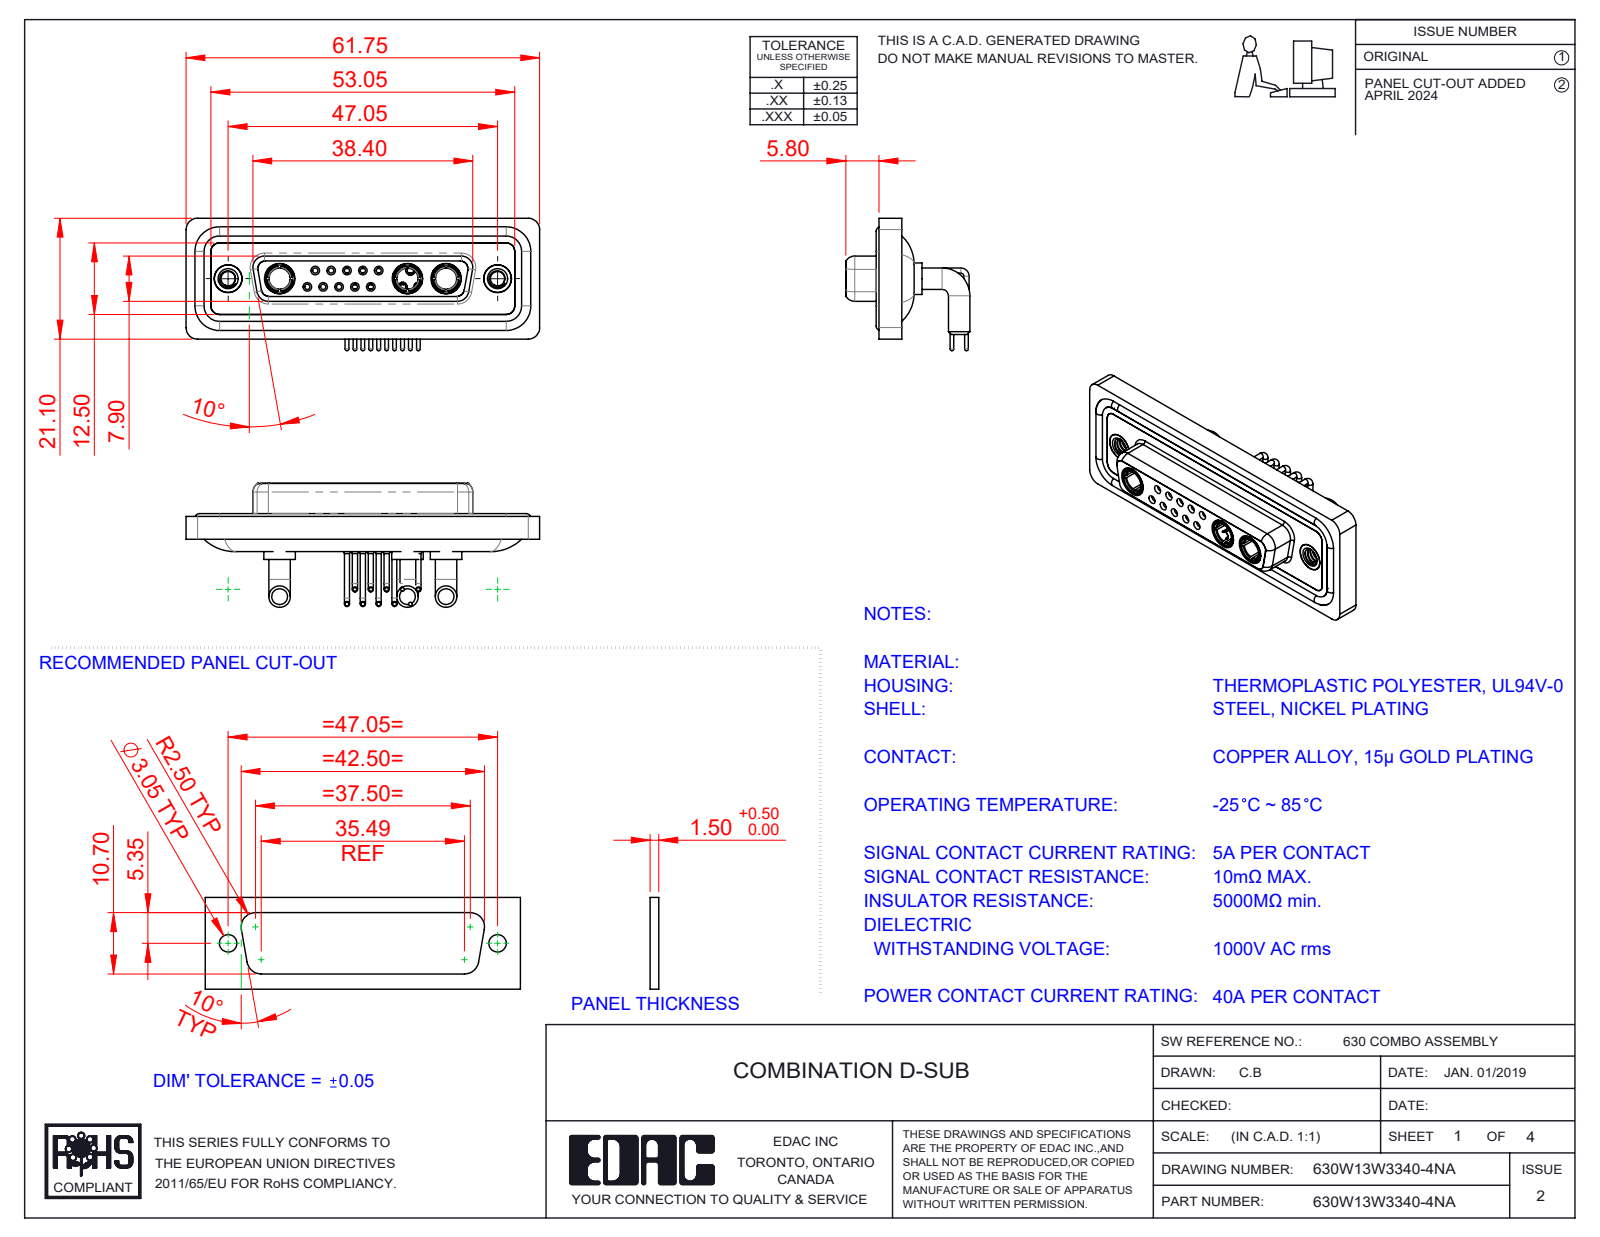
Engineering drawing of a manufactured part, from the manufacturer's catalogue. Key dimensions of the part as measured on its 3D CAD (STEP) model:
Part name (STEP PRODUCT): 630Combo Contact Row 1_50 Contacts; 630Combo Waterproof Housing_25 Contacts; 630Combo Contact Row 2_50 Contacts; 630Combo Housing_13W3 (+5 more)
STEP written by: SolidWorks 2023 (CONFIG_CONTROL_DESIGN)
Units: millimetres
Bodies: 23 solids, 1144 faces (342 planar, 491 cylindrical, 311 other)
Overall size (bounding box): 61.75 × 23.12 × 21.68
Volume: 8 681 mm³ · Surface area: 14 431 mm²
Round holes (diameter × count): ⌀0.9 ×10, ⌀1.1 ×10, ⌀1.5 ×10, ⌀2 ×10, ⌀1.6 ×5, ⌀1.7 ×5, ⌀4.85 ×5, ⌀3.7 ×3, ⌀5.3 ×3, ⌀2.5 ×2, ⌀4 ×2, ⌀4.05 ×2
Round bosses / shafts (diameter × count): ⌀0.9 ×15, ⌀1.6 ×12, ⌀0.65 ×10, ⌀3.75 ×6, ⌀2 ×5, ⌀1.5 ×5, ⌀5.5 ×3, ⌀5.2 ×3
Partial cylindrical surfaces — rounded edges, fillets, slot ends (radius × count): R1.5 ×18, R2 ×18, R1.35 ×8, R1.6 ×8, R0.25 ×4, R0.5 ×4, R0.6 ×4, R0.65 ×4
Main face-to-face distances: 0.4, 1.8, 4.1, 1.1, 1.6, 3.1, 2.5, 1.5, 3.7, 1.4
Hole centre spacings: 3.16, 2.77, 5.54, 5.04, 8.31, 5.03, 7.49, 11.08
